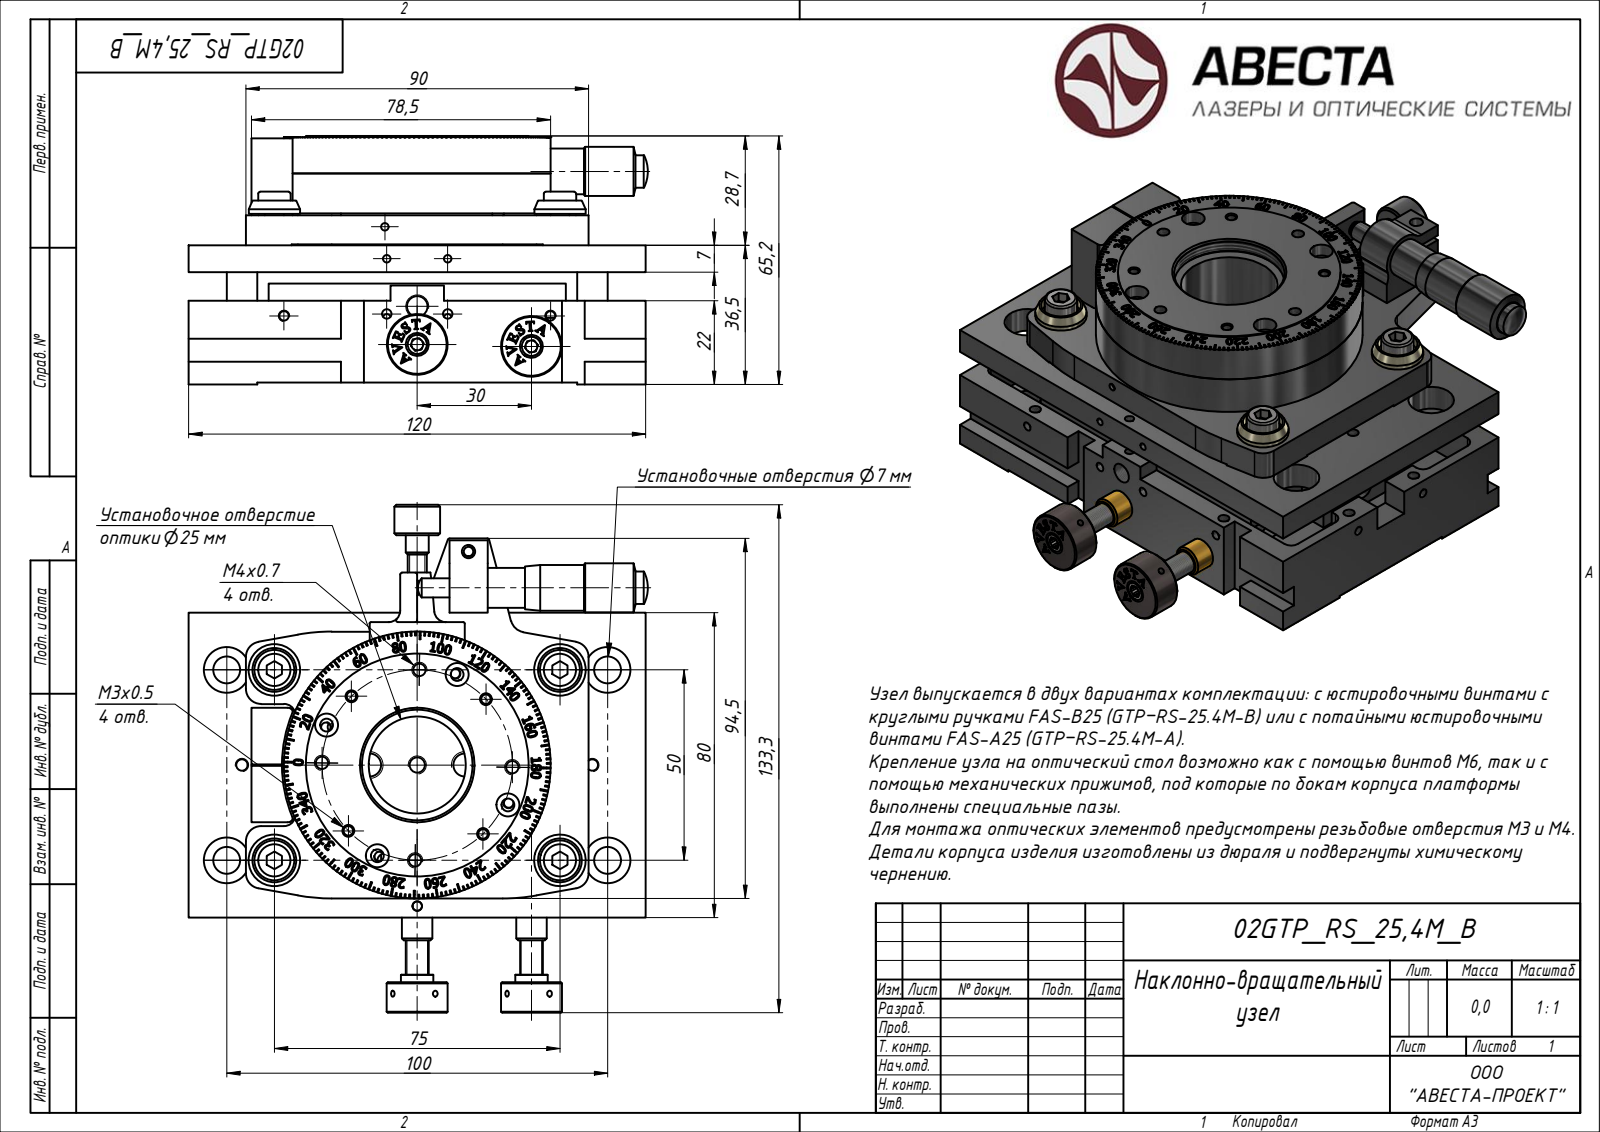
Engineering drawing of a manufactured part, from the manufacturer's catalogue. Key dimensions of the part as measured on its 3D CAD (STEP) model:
Part name (STEP PRODUCT): Block 01; Block 02; Block 03; Block 04 (+3 more)
STEP written by: ST-DEVELOPER v15 (AUTOMOTIVE_DESIGN)
Units: millimetres
Bodies: 16 solids, 3149 faces (0 planar, 0 cylindrical, 3149 other)
Overall size (bounding box): 133.3 × 120.5 × 65.2
Volume: 45 358 mm³ · Surface area: 128 896 mm²
